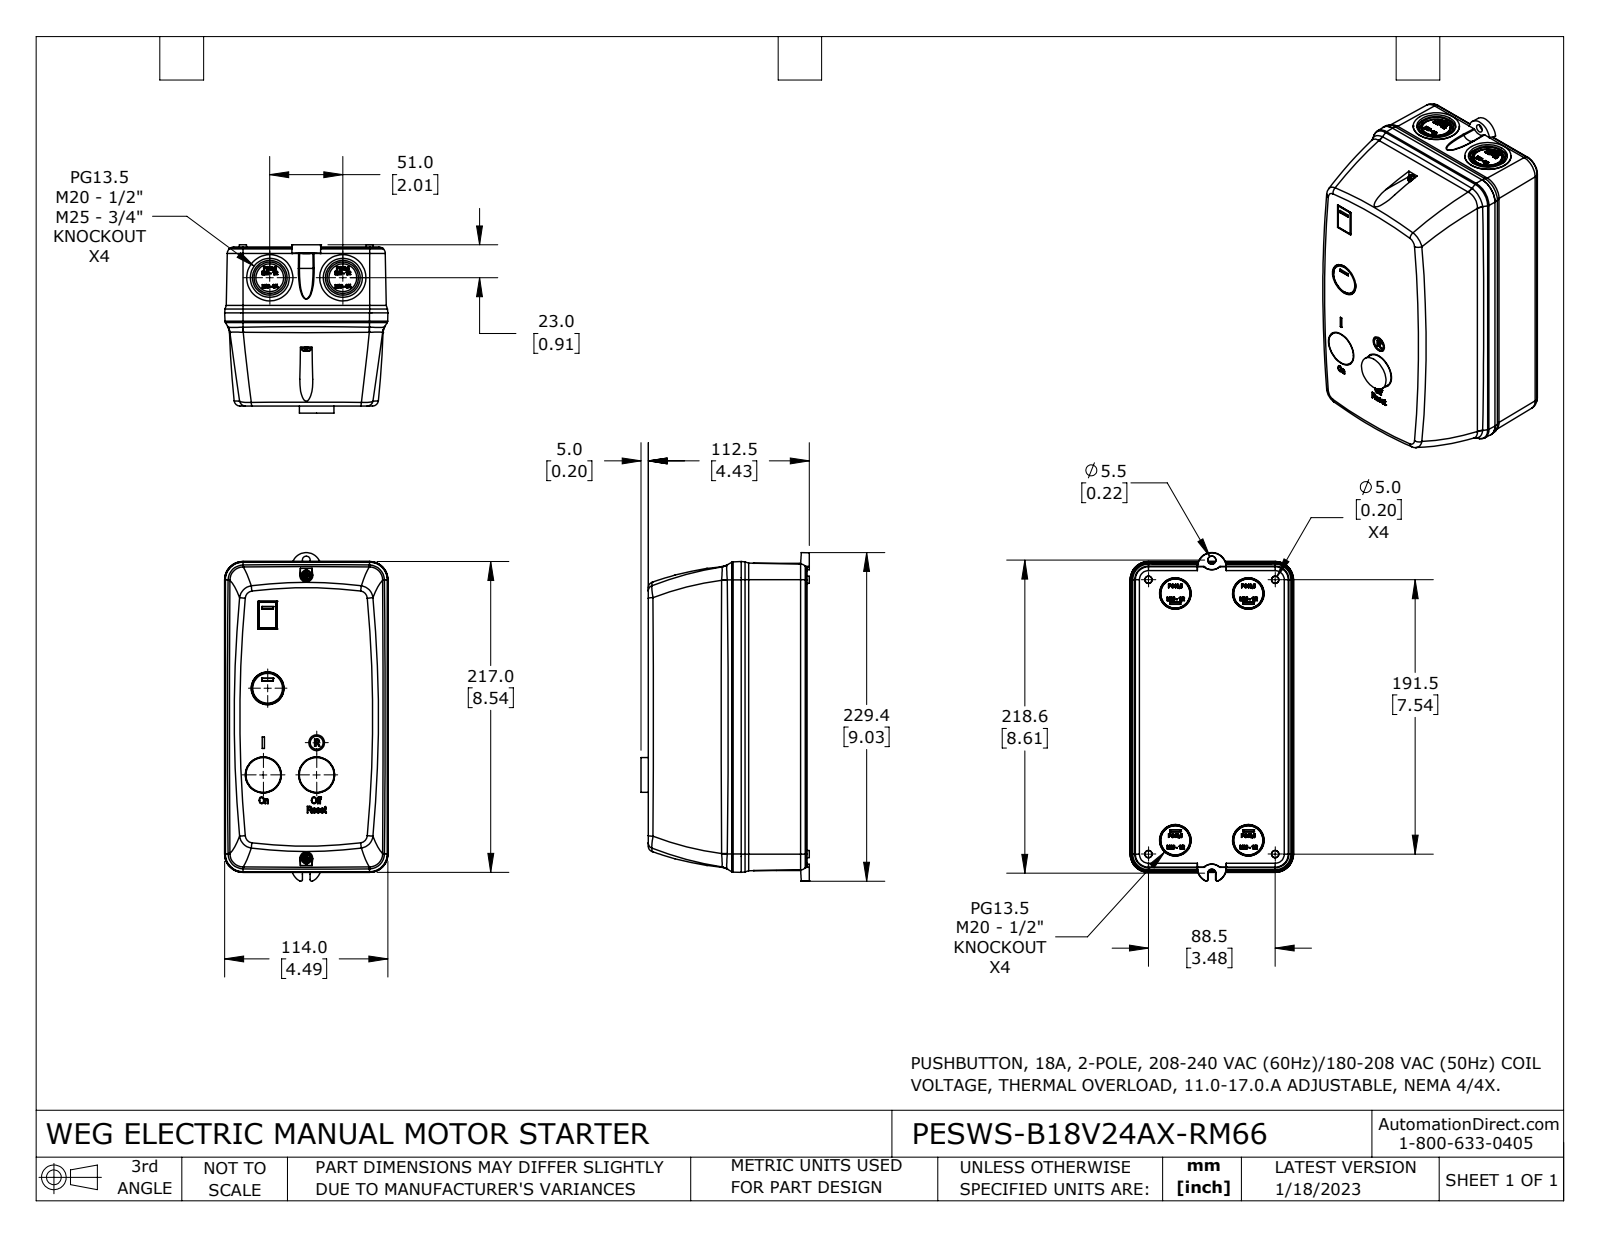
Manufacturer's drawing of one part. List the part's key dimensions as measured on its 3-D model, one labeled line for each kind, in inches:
Part name (STEP PRODUCT): PESWS-B18V24AX-RM66
STEP written by: SolidWorks 2021 (CONFIG_CONTROL_DESIGN)
Units: inches
Bodies: 6 solids, 2195 faces (1110 planar, 92 cylindrical, 993 other)
Overall size (bounding box): 9.033 × 4.626 × 4.489
Volume: 149.9 in³ · Surface area: 257.6 in²
Round holes (diameter × count): ⌀0.173 ×2, ⌀0.863 ×2, ⌀1.072 ×2, ⌀0.217 ×1, ⌀0.433 ×1
Round bosses / shafts (diameter × count): ⌀1.27 ×2, ⌀0.955 ×2, ⌀0.953 ×2, ⌀0.763 ×2, ⌀0.276 ×2, ⌀0.118 ×2, ⌀0.354 ×1
Partial cylindrical surfaces — rounded edges, fillets, slot ends (radius × count): R0.079 ×4, R0.181 ×4, R0.376 ×4, R0.257 ×2, R0.297 ×2, R0.082 ×1, R0.085 ×1, R0.108 ×1
Main face-to-face distances: 1.811, 2.559, 4.37, 0.02, 4.35, 1.791, 4.331, 0.039, 4.311, 2.52
Hole centre spacings: 0.413, 2.008, 3.202, 4.615, 5.028, 7.795, 8.209
